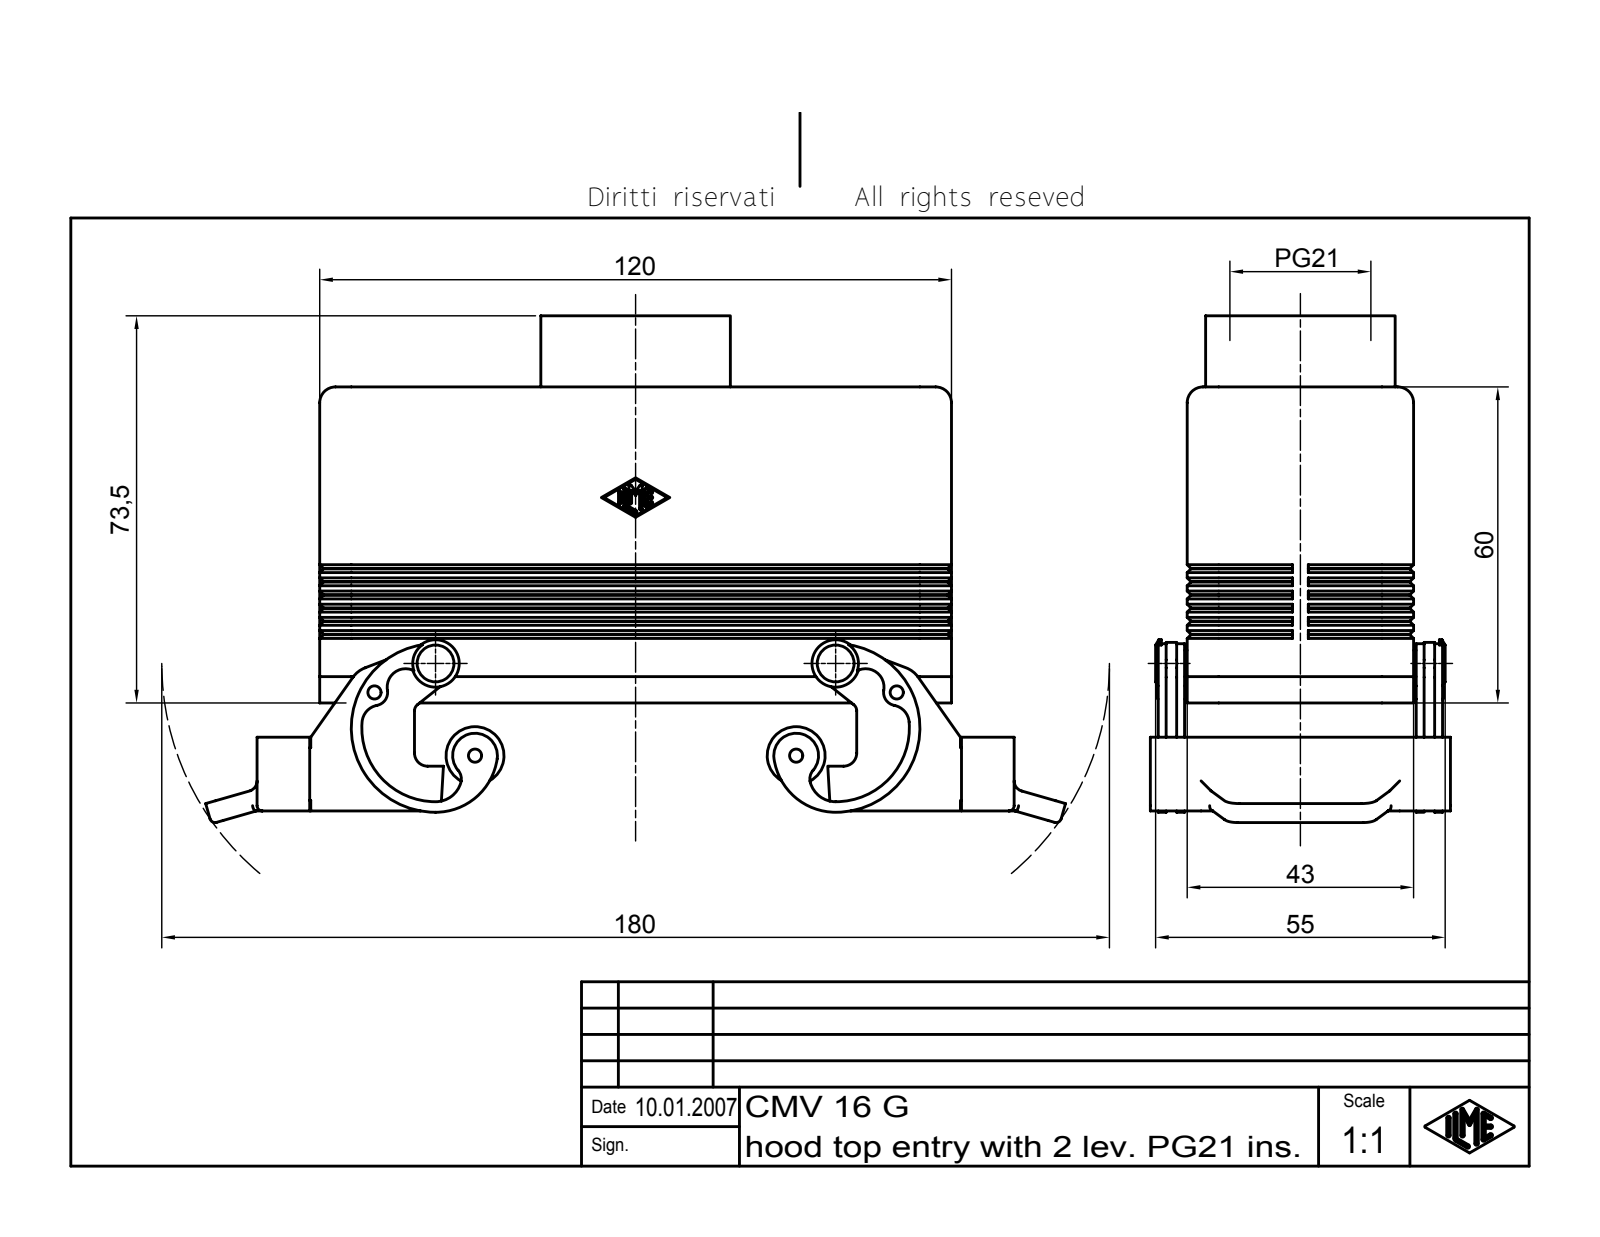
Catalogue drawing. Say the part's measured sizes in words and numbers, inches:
The part is named "CHV Tüllengehäuse 2 Bügel für einen Einsatz". Its 3-D file was written by "Autodesk Inventor 7 (AUTOMOTIVE_DESIGN)". It is 1 solid with 923 faces: 285 planar, 235 cylindrical and 403 other. Overall it measures 6.43 by 3.788 by 2.244 inches. Its volume is 6.419 cubic inches and its surface area 101.7 square inches. Round holes: 2 of diameter 0.098, 1 of diameter 0.851, 1 of diameter 1.054. Round bosses or shafts: 2 of diameter 0.433, 2 of diameter 0.354, 2 of diameter 0.197, 2 of diameter 0.079, 1 of diameter 1.417. Partial cylindrical surfaces (rounded edges, fillets, slot ends): 14 of radius 0.01, 12 of radius 0.118, 10 of radius 0.079, 8 of radius 0.039, 6 of radius 0.098, 4 of radius 0.118, 4 of radius 0.138, 4 of radius 0.197. The main face-to-face distances are 0.118, 1.575, 1.457, 1.693, 0.335, 0.453, 4.606, 0.07, 0.079, 0.157. The hole center spacings are 3.906.
